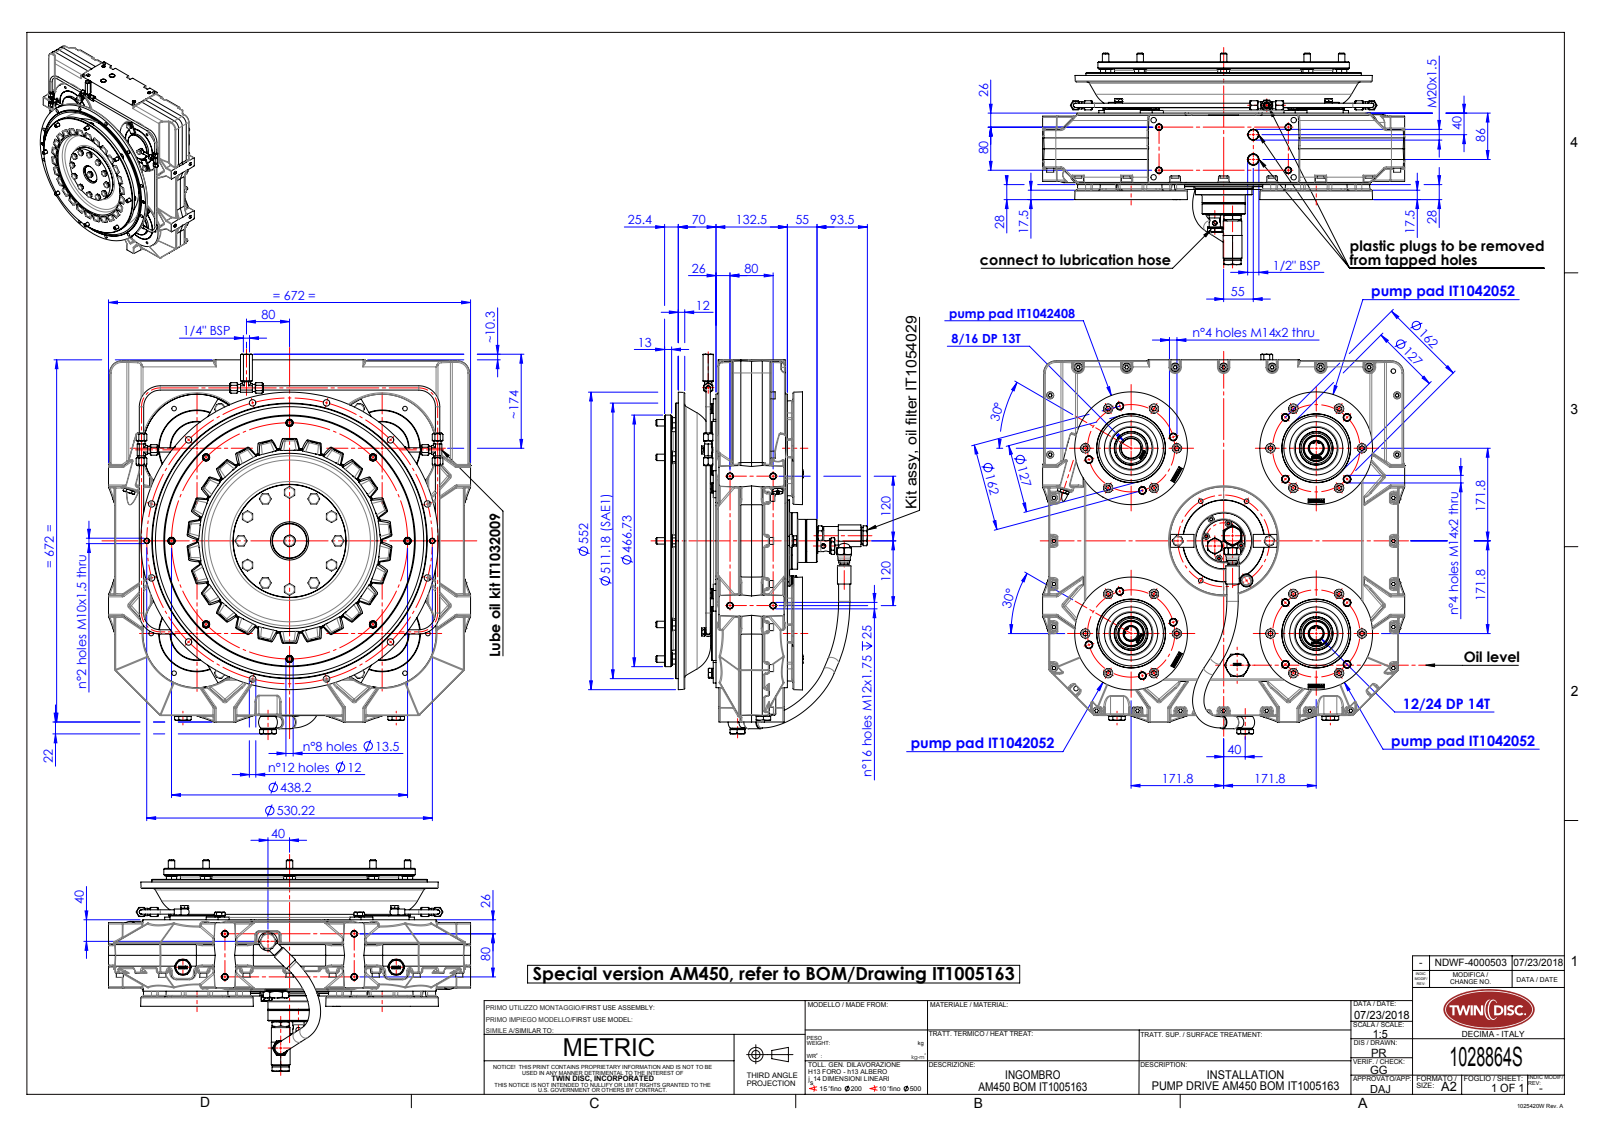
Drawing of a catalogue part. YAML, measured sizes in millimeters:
part_name: "IT1042052_rev00-installation; IT1032009-installation; IT1071114-installation; IT2021216_rev03-installation (+5 more)"
step_written_by: "SolidWorks 2015 (AUTOMOTIVE_DESIGN)"
units: millimeters
bodies: {solids: 86, faces: 11023, planar: 4780, cylindrical: 3108, other: 3135}
overall_size: [704.25, 672.41, 392.4]
volume: 13240000
surface_area: 4964000
round_holes:
  - {diameter: 8.5, count: 70}
  - {diameter: 11, count: 36}
  - {diameter: 12, count: 36}
  - {diameter: 13, count: 30}
  - {diameter: 10.2, count: 26}
  - {diameter: 17, count: 24}
  - {diameter: 14, count: 20}
  - {diameter: 10, count: 15}
  - {diameter: 7, count: 11}
  - {diameter: 16, count: 11}
  - {diameter: 8, count: 9}
  - {diameter: 5, count: 8}
round_bosses_or_shafts:
  - {diameter: 10, count: 37}
  - {diameter: 13, count: 33}
  - {diameter: 8, count: 33}
  - {diameter: 12, count: 31}
  - {diameter: 18, count: 29}
  - {diameter: 16, count: 24}
  - {diameter: 24, count: 21}
  - {diameter: 18.1, count: 11}
partial_cylinders:
  - {radius: 2.5, count: 428}
  - {radius: 2, count: 156}
  - {radius: 1.5, count: 131}
  - {radius: 3, count: 100}
  - {radius: 0.45, count: 58}
  - {radius: 60, count: 52}
  - {radius: 5, count: 24}
  - {radius: 10.97, count: 12}
face_to_face_distances: [128.5, 4, 12, 10, 124.5, 132.5, 20, 99.4, 24, 152.5]
hole_center_spacings: [120, 57.4, 75, 138.58, 178.39, 207.84, 240, 16.4]
